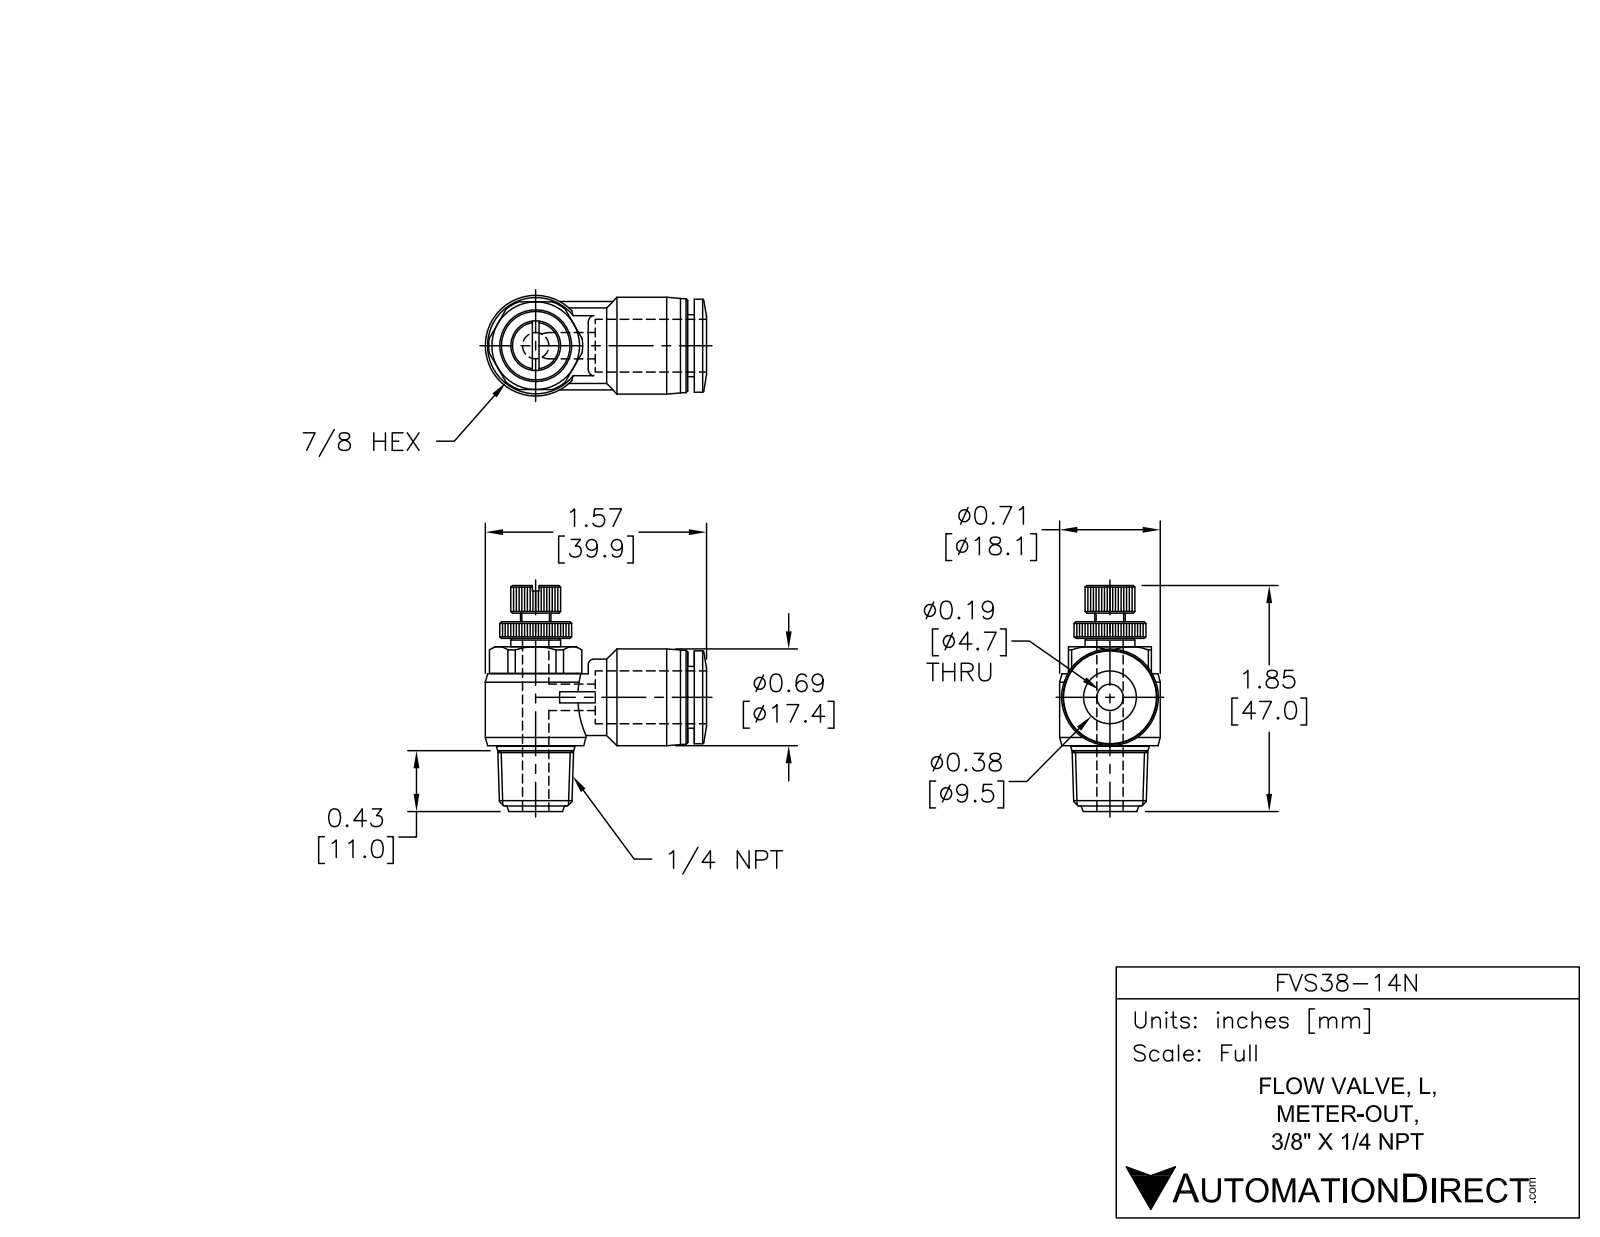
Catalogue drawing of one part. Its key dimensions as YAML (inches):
part_name: "FVS38-14N"
step_written_by: "SolidWorks 2015 (AUTOMOTIVE_DESIGN)"
units: inches
bodies: {solids: 1, faces: 427, planar: 188, cylindrical: 113, other: 126}
overall_size: [1.85, 1.575, 0.717]
volume: 0.586
surface_area: 8.222
round_holes:
  - {diameter: 0.177, count: 2}
  - {diameter: 0.386, count: 1}
round_bosses_or_shafts:
  - {diameter: 0.717, count: 1}
  - {diameter: 0.689, count: 1}
  - {diameter: 0.669, count: 1}
  - {diameter: 0.661, count: 1}
  - {diameter: 0.591, count: 1}
  - {diameter: 0.543, count: 1}
  - {diameter: 0.539, count: 1}
  - {diameter: 0.441, count: 1}
partial_cylinders:
  - {radius: 0.256, count: 1}
  - {radius: 0.335, count: 1}
face_to_face_distances: [0.705, 0.047, 0.177, 0.882, 0.624, 0.512, 0.193, 0.37, 0.764, 0.252]
